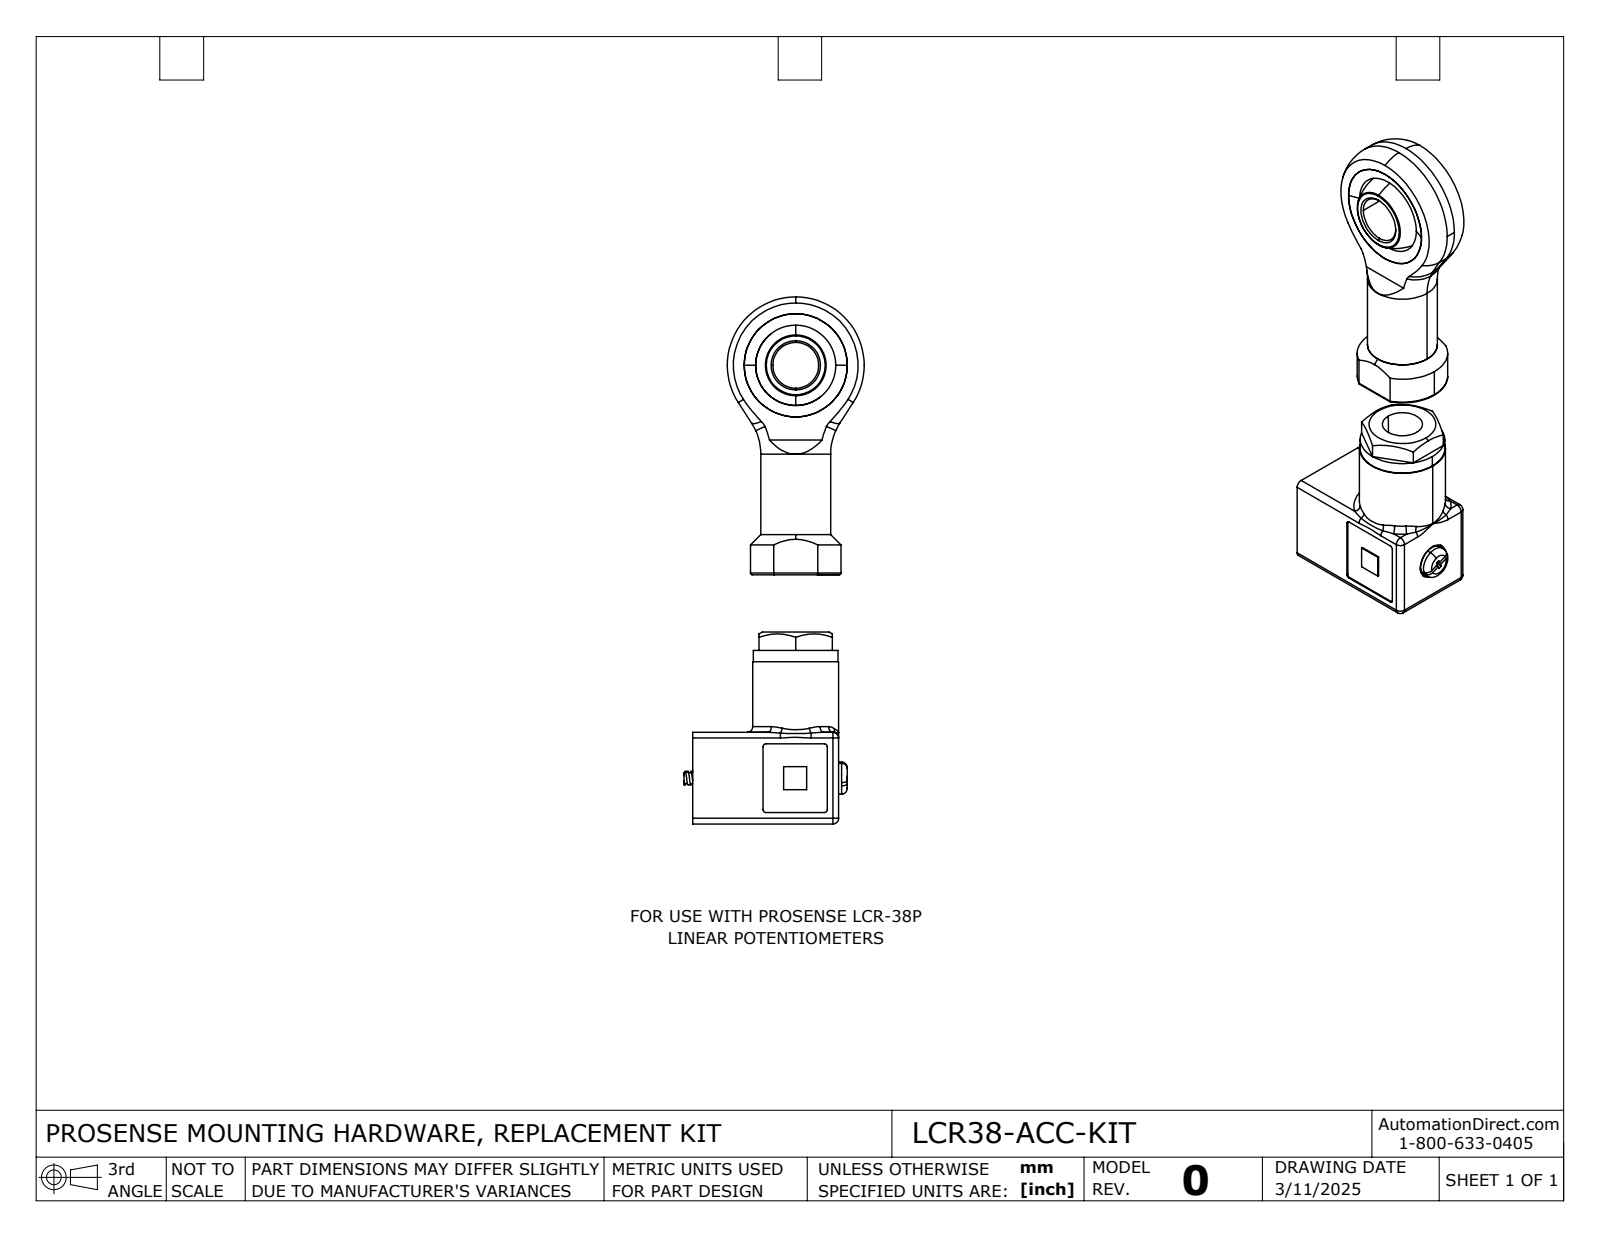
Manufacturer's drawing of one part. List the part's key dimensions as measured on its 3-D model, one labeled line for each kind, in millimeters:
Part name (STEP PRODUCT): LCR38-ACC-KIT
STEP written by: SolidWorks 2024 (AUTOMOTIVE_DESIGN)
Units: millimetres
Bodies: 8 solids, 362 faces (140 planar, 147 cylindrical, 75 other)
Overall size (bounding box): 92 × 31.45 × 16.2
Volume: 9 603 mm³ · Surface area: 12 140 mm²
Round holes (diameter × count): ⌀8 ×2, ⌀2.75 ×1, ⌀3 ×1, ⌀6.2 ×1, ⌀11.4 ×1, ⌀14 ×1, ⌀18 ×1
Round bosses / shafts (diameter × count): ⌀15 ×1, ⌀14.78 ×1, ⌀12.2 ×1, ⌀5.6 ×1, ⌀2.37 ×1, ⌀2.15 ×1
Partial cylindrical surfaces — rounded edges, fillets, slot ends (radius × count): R1 ×16, R0.5 ×4, R0.3 ×2, R10 ×2, R7.9 ×1, R11.95 ×1
Main face-to-face distances: 0.8, 15.2, 14.4, 12.3, 16, 11.5, 3.7, 2.9, 0.6, 15
